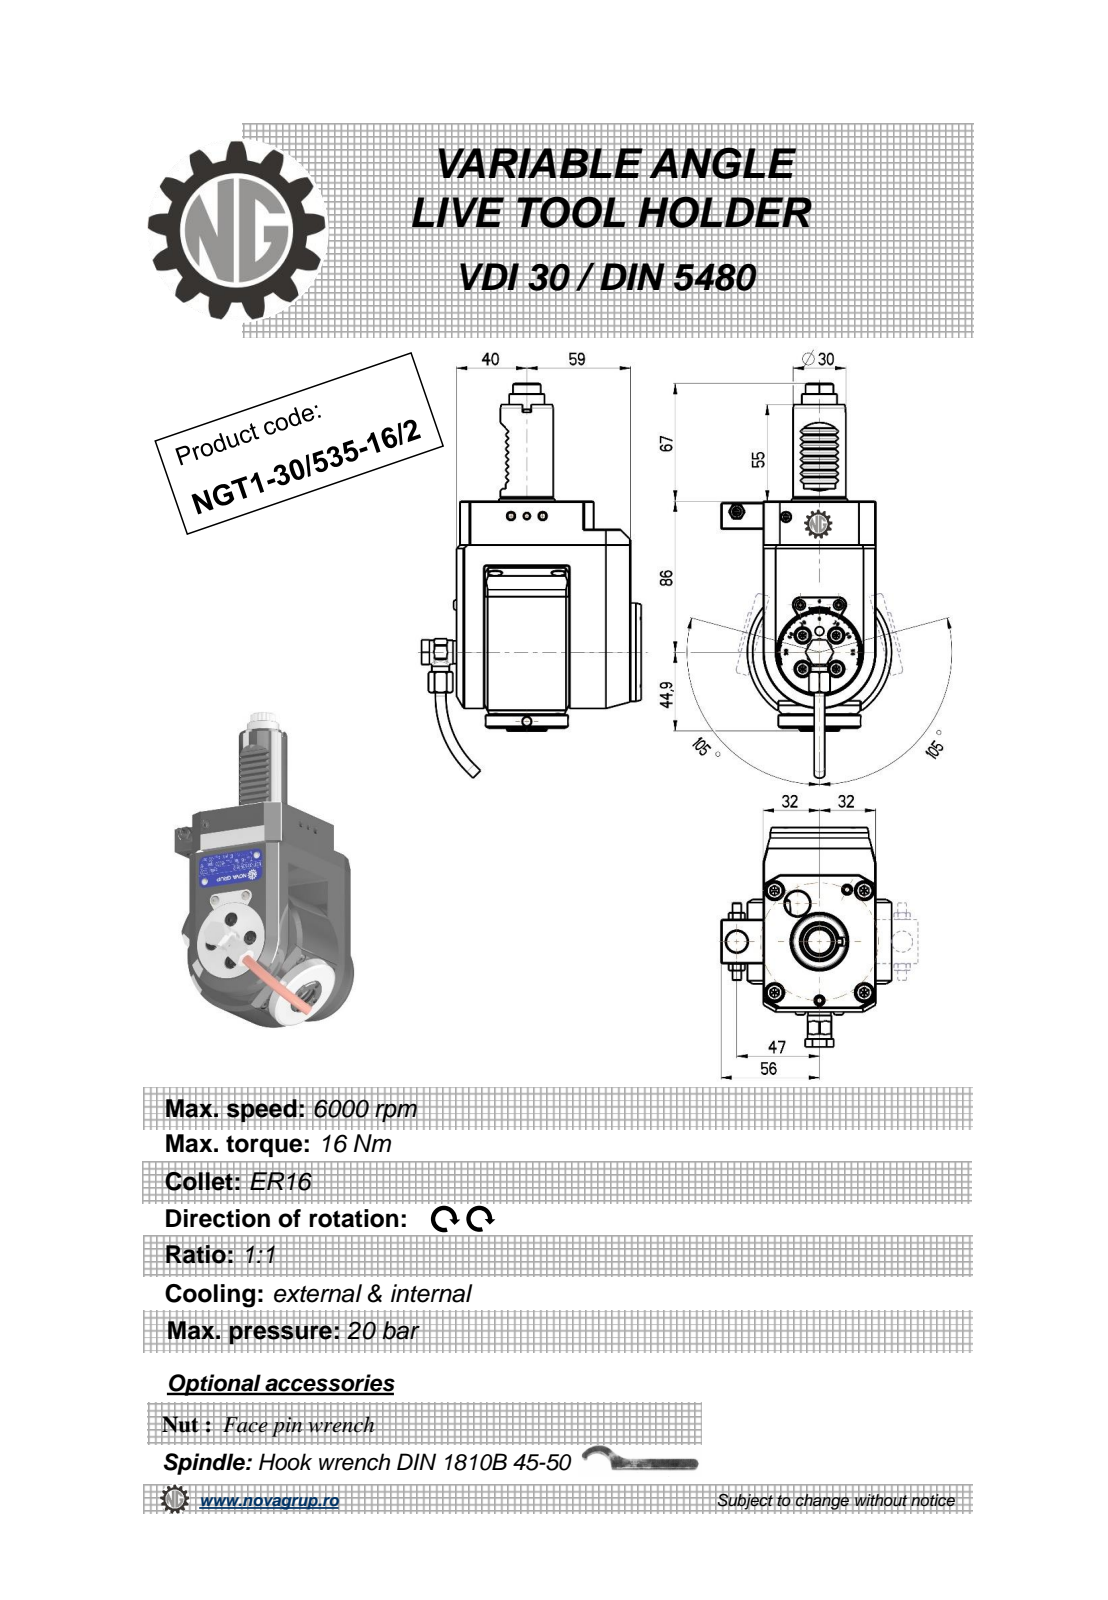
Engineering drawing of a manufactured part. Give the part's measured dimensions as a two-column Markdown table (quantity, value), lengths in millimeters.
| quantity | value |
| --- | --- |
| part name | NGT1_30_535_16_2 |
| STEP written by | PRO/ENGINEER BY PARAMETRIC TECHNOLOGY CORPORATION, 2010280 (CONFIG_CONTROL_DESIGN) |
| units | millimeters |
| bodies | 1 solid, 588 faces (212 planar, 209 cylindrical, 167 other) |
| overall size | 224.67 × 124.9 × 97 |
| volume | 780 866 mm³ |
| surface area | 72 475 mm² |
| round holes (diameter × count) | 3.2 × 4, 4 × 3, 5 × 2, 3 × 1, 4.2 × 1, 6.2 × 1, 9 × 1, 9.5 × 1, 11 × 1, 12 × 1, 12.5 × 1 |
| round bosses / shafts (diameter × count) | 10 × 2, 6 × 2, 5.7 × 2, 56 × 1, 47 × 1, 35 × 1, 30 × 1, 23 × 1 |
| partial cylindrical surfaces (radius × count) | 1.98 × 36, 0.26 × 12, 0.3 × 8, 0.16 × 6, 0.5 × 4, 1 × 2, 7.29 × 1, 7.7 × 1 |
| main face-to-face distances | 64, 16, 37, 99, 6, 105, 21, 14, 62, 83 |
| hole center spacings | 9.25, 13.08, 18.5, 47.9, 49.87, 50.26, 0.4, 37.75 |
